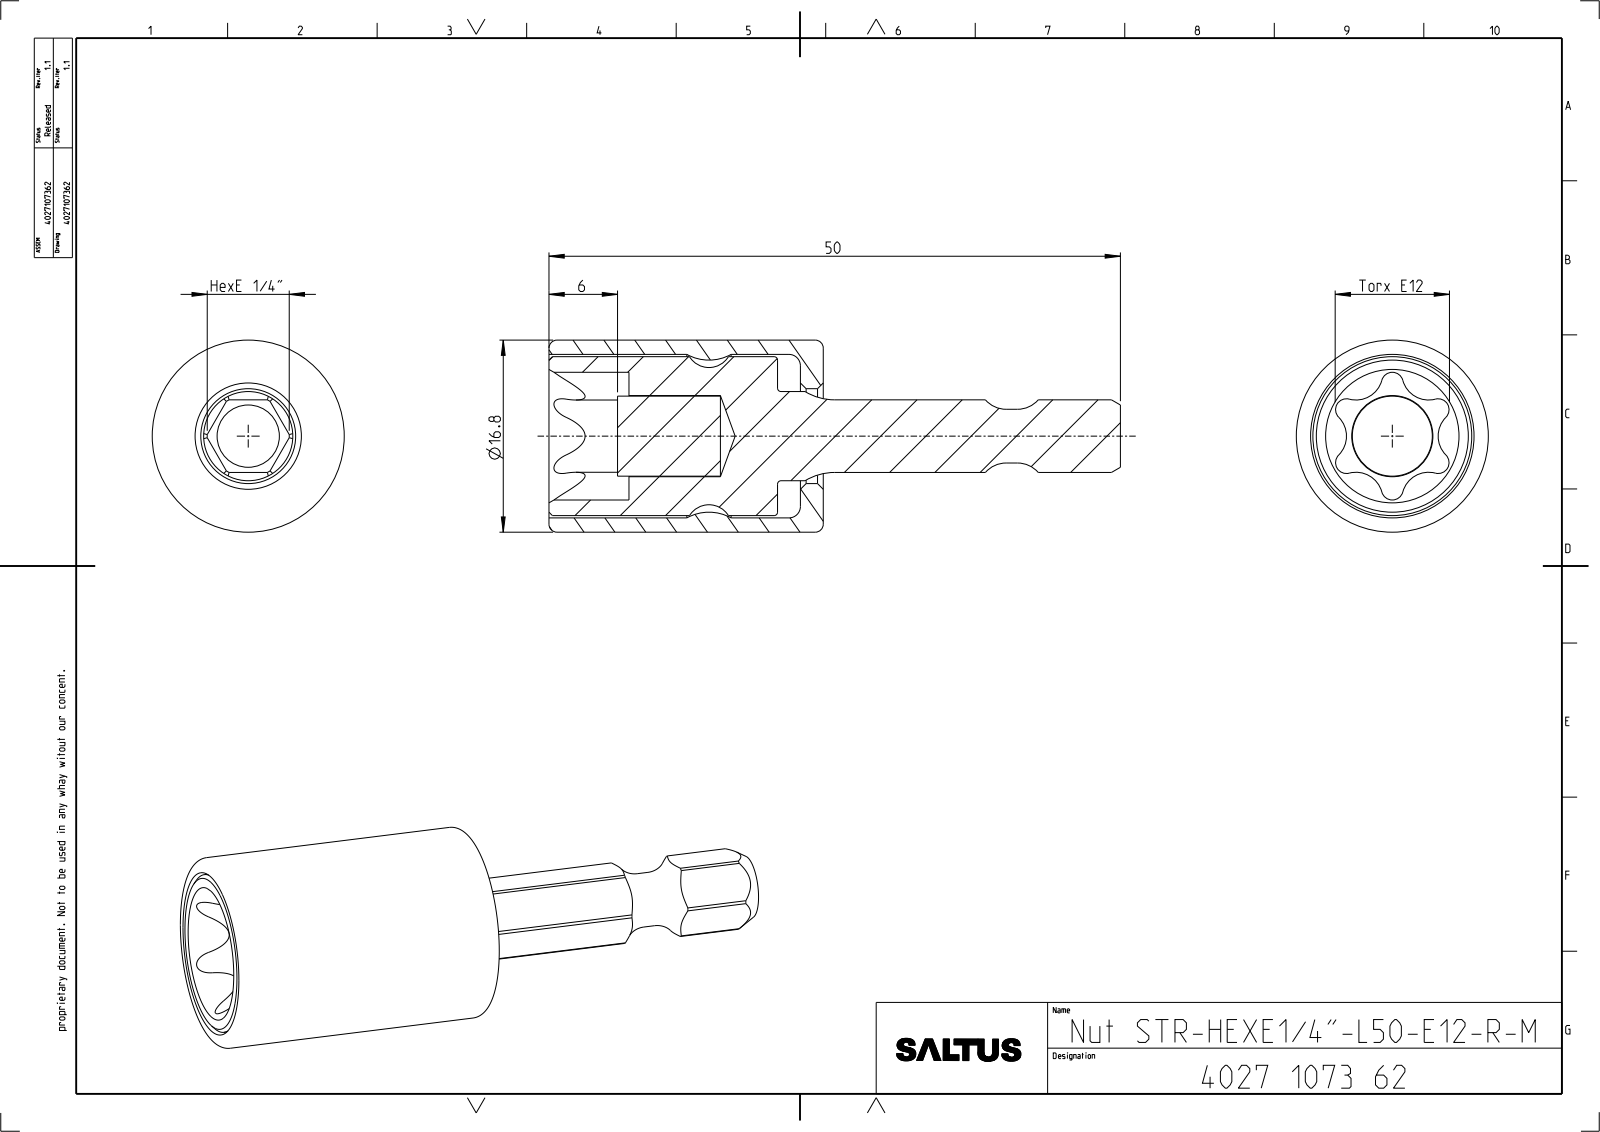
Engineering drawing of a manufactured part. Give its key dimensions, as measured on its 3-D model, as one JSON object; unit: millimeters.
{"part_name": "4027911289; 4027040395; 4027107362_ASM", "step_written_by": "CREO PARAMETRIC BY PTC INC, 2022414 (CONFIG_CONTROL_DESIGN)", "units": "millimeters", "bodies": {"solids": 3, "faces": 107, "planar": 21, "cylindrical": 50, "other": 36}, "overall_size": [50, 16.9, 16.9], "volume_mm3": 5189, "surface_area_mm2": 5072, "round_holes": [[7.1, 1], [8.3, 1], [14.4, 1]], "round_bosses_or_shafts": [[16.9, 1], [13.9, 1], [7.8, 1], [7, 1], [4.7, 1]], "partial_cylinders_radius": [[0.95, 6], [2.34, 6], [5, 6], [3.59, 1]], "face_to_face_distances": [6.34, 2, 4, 9, 7, 15, 6.36, 24, 20, 22]}
